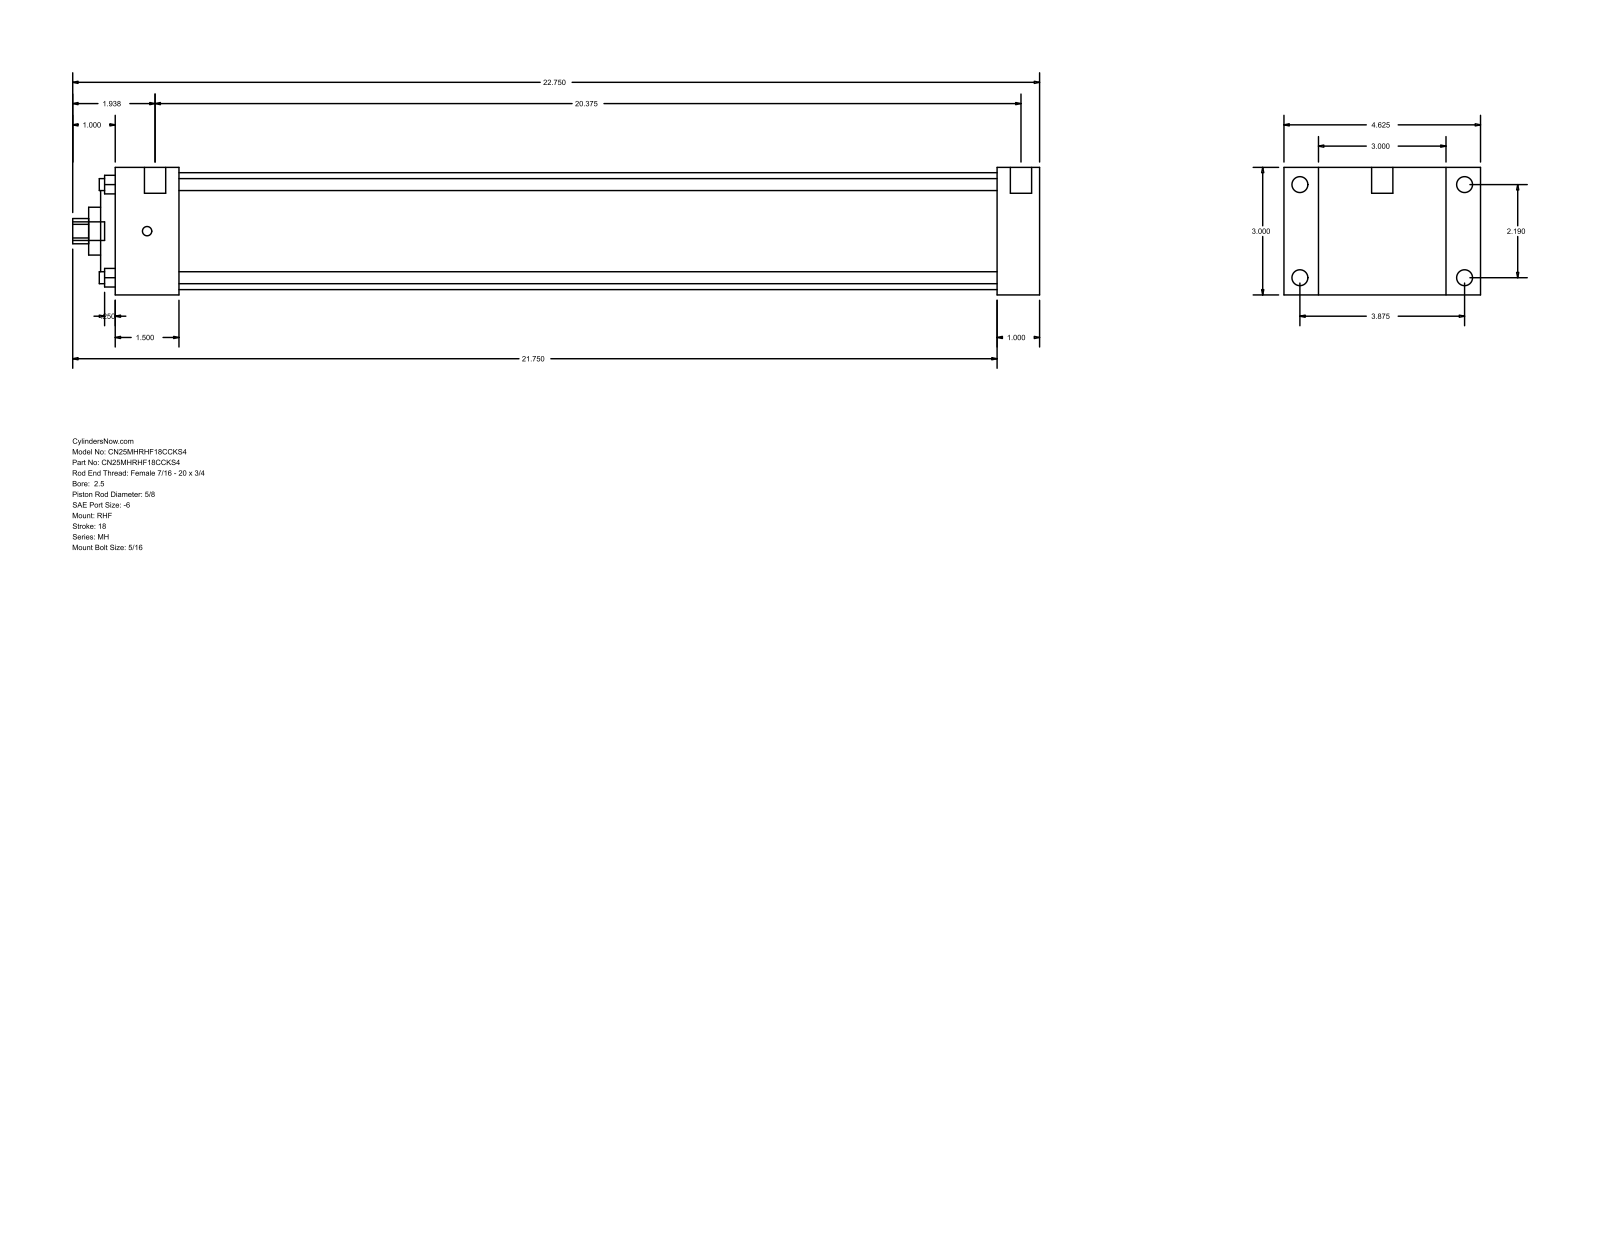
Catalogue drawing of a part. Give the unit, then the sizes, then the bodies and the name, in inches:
Units: inches
Overall size (bounding box): 22.75 × 4.625 × 3
Round holes (diameter × count): ⌀0.281 ×4, ⌀0.625 ×1, ⌀1.125 ×1, ⌀2.187 ×1, ⌀2.75 ×1
Round bosses / shafts (diameter × count): ⌀0.375 ×4, ⌀0.219 ×4, ⌀0.5 ×2, ⌀0.437 ×1
Partial cylindrical surfaces — rounded edges, fillets, slot ends (radius × count): R0.297 ×1
Main face-to-face distances: 3, 1, 0.813, 3.813, 21.75, 20.75, 4.625, 1.5, 19.25, 20.25
Hole centre spacings: 1.548, 2.19, 3.097
Bodies: 0 solids, 90 faces (61 planar, 29 cylindrical, 0 other)
Part name (STEP PRODUCT): MH_RHF__0250_0.625
STEP written by: GSSL Pune (CONFIG_CONTROL_DESIGN)
